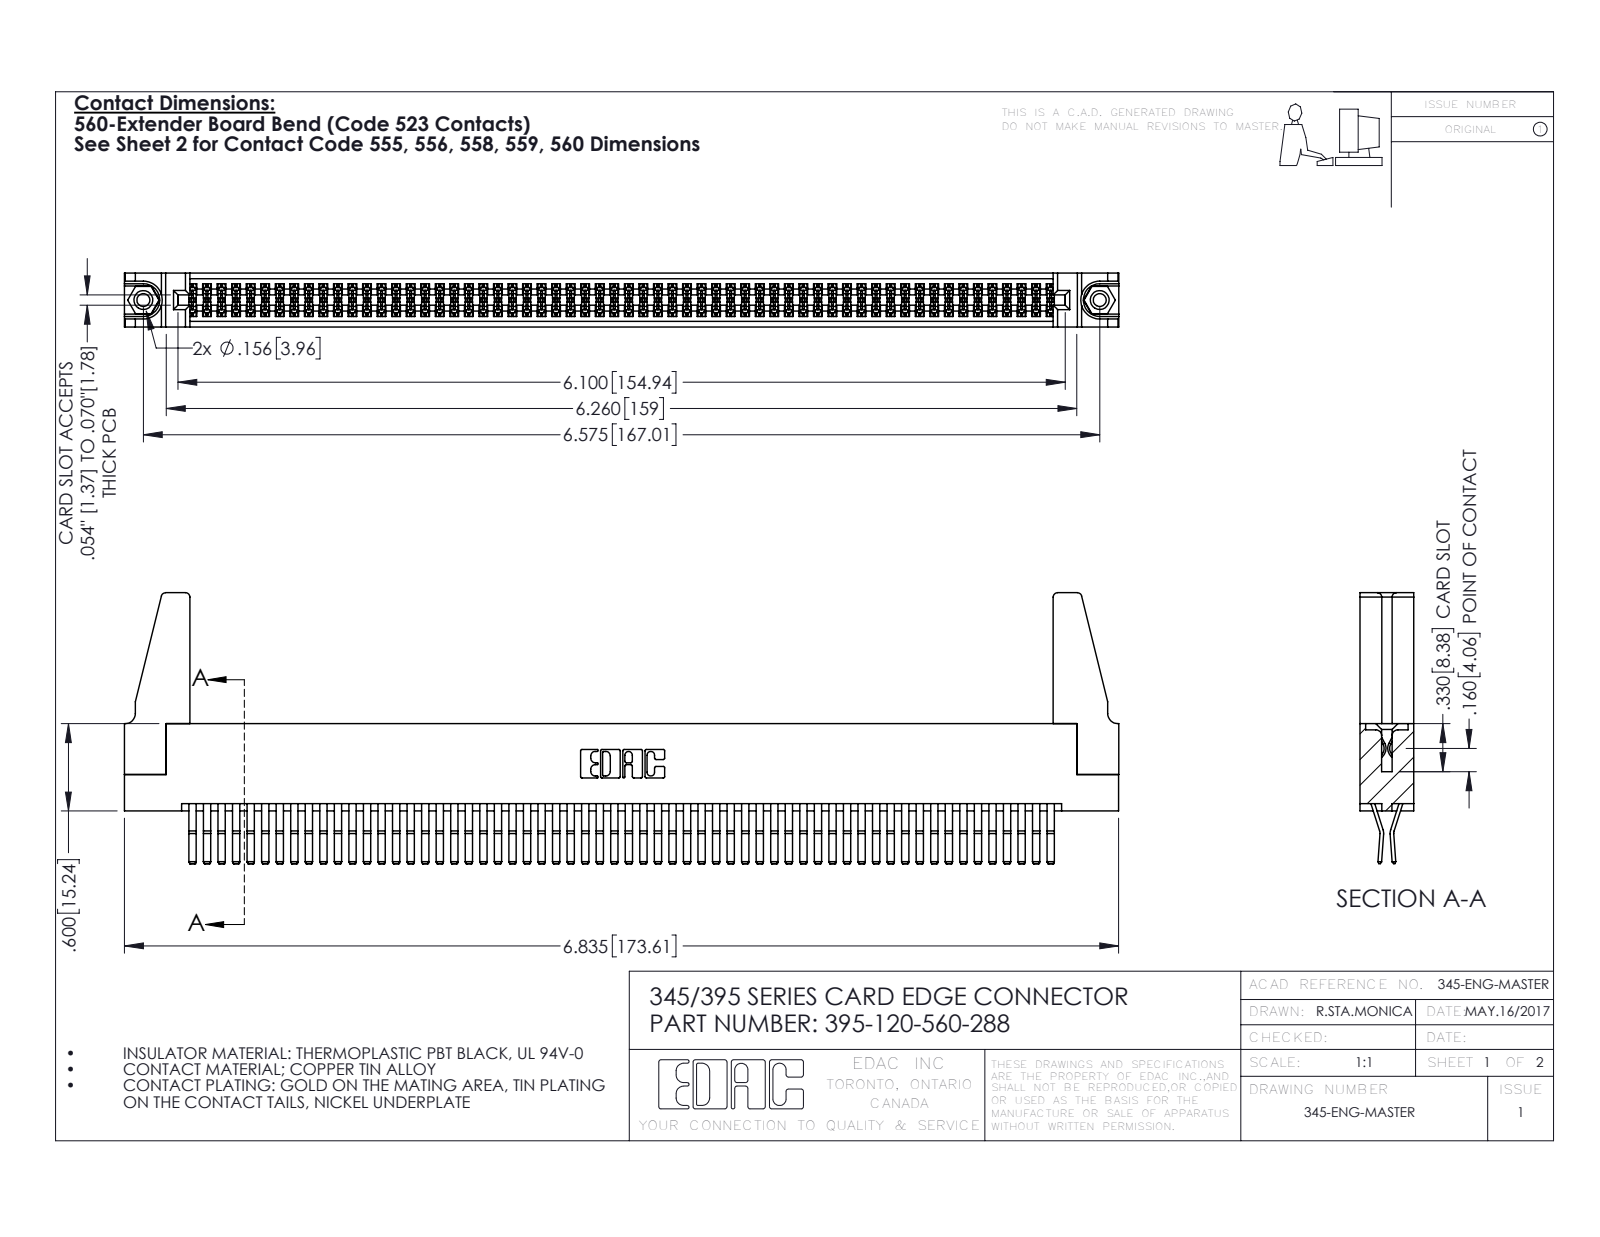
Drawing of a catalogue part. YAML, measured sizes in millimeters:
part_name: "345 Part_Flush Mounting Lugs - 0.156 Dia-TH; 345-250-001_345-250-001-102; 345-220-078_345-220-088; 395-120-560-288 (+1 more)"
step_written_by: "SolidWorks 2016 (CONFIG_CONTROL_DESIGN)"
units: millimeters
bodies: {solids: 125, faces: 6490, planar: 4112, cylindrical: 2362, other: 16}
overall_size: [173.6, 47.3, 9.4]
volume: 21070
surface_area: 31840
round_holes:
  - {diameter: 2.3, count: 2}
  - {diameter: 3.2, count: 2}
  - {diameter: 4, count: 2}
  - {diameter: 1.6, count: 1}
round_bosses_or_shafts:
  - {diameter: 3.9, count: 2}
partial_cylinders:
  - {radius: 0.2, count: 180}
  - {radius: 0.3, count: 22}
  - {radius: 0.8, count: 8}
  - {radius: 0.2, count: 6}
  - {radius: 0.8, count: 6}
  - {radius: 0.7, count: 3}
  - {radius: 0.3, count: 2}
  - {radius: 0.4, count: 2}
face_to_face_distances: [1.8, 7.6, 0.6, 9.4, 5.1, 2.5, 6.9, 5.7, 4.4, 3.8]
hole_center_spacings: [6.9, 161, 167]
